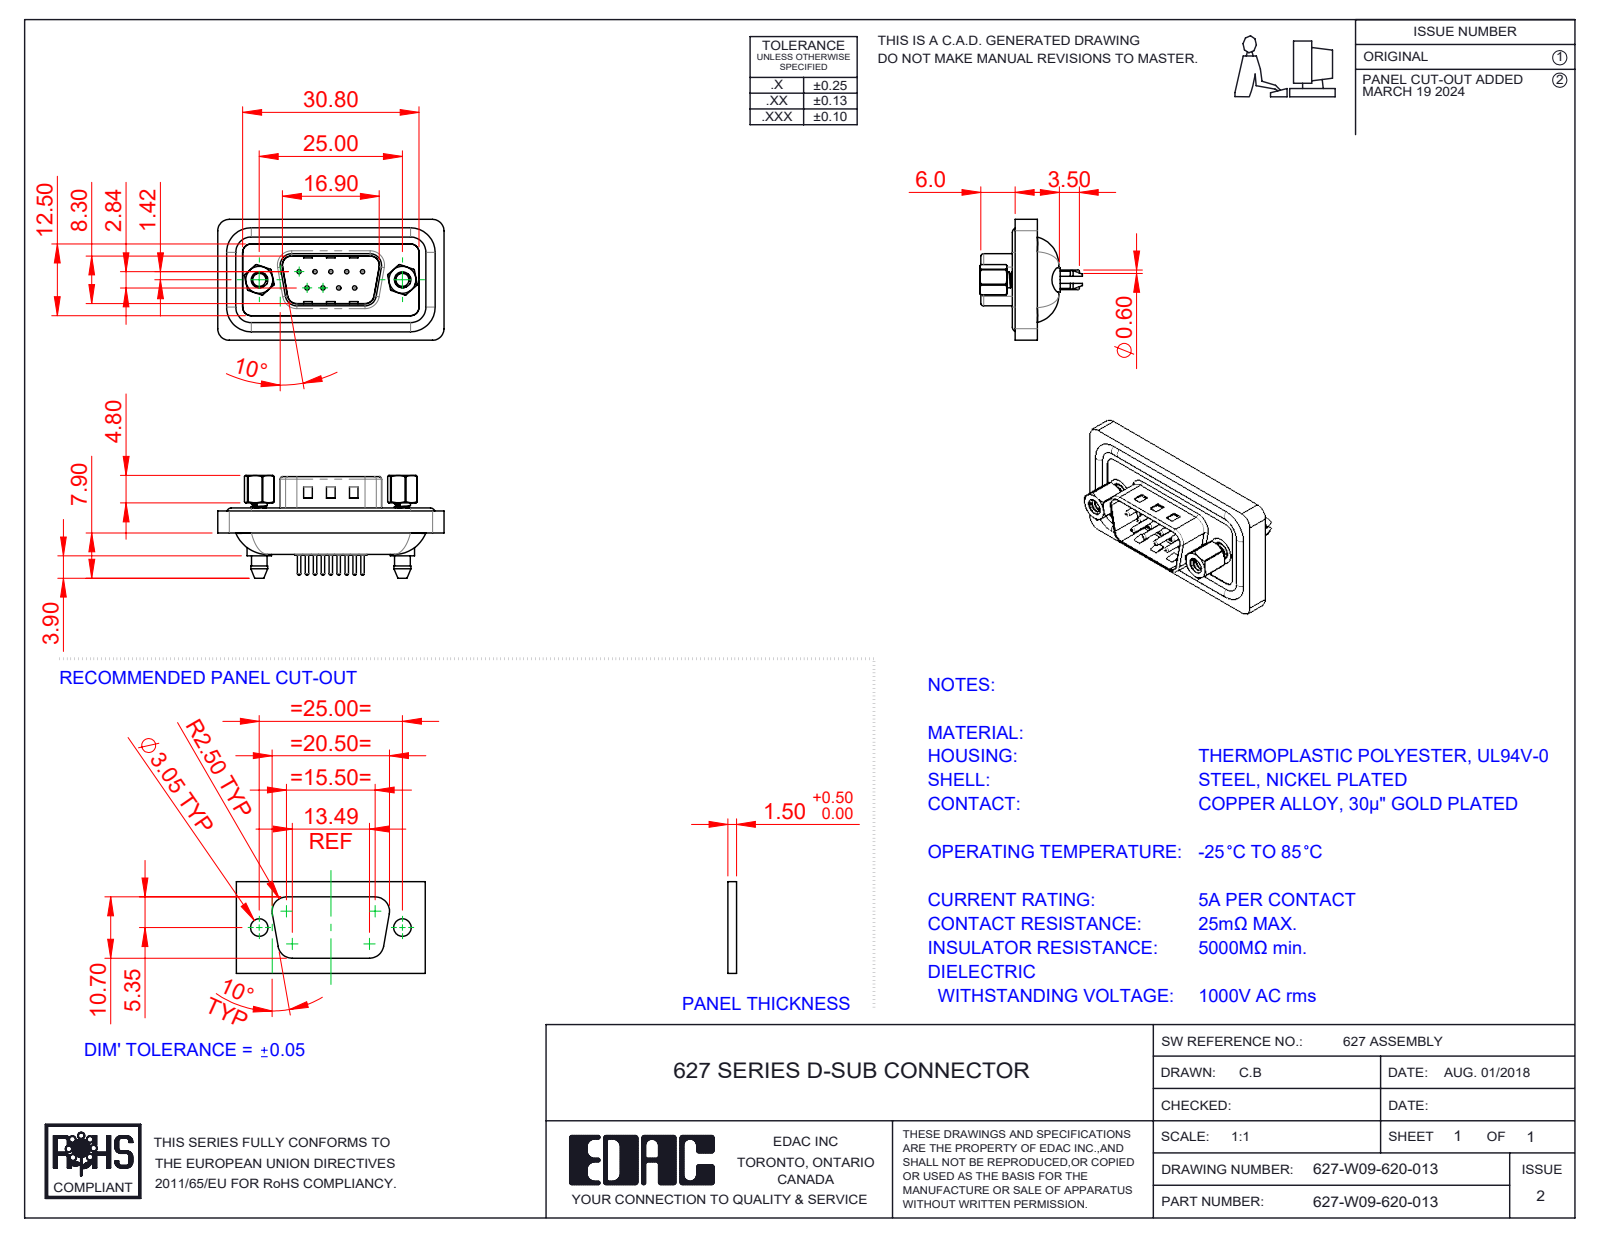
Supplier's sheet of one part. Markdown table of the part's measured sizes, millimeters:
| quantity | value |
| --- | --- |
| part name | 627W Contact Row 2_20; 627W Housing_09 Contacts; 627W Waterproof Housing_09 Contacts BL; 627-W09-620-013 (+4 more) |
| STEP written by | SolidWorks 2020 (CONFIG_CONTROL_DESIGN) |
| units | millimeters |
| bodies | 17 solids, 847 faces (218 planar, 388 cylindrical, 241 other) |
| overall size | 39.5 × 21.1 × 17.75 |
| volume | 4 719 mm³ |
| surface area | 6 930 mm² |
| round holes (diameter × count) | 0.75 × 9, 1.5 × 9, 1.6 × 9, 2 × 9, 2.26 × 2, 2.29 × 2, 4 × 2, 4.25 × 2, 4.8 × 2 |
| round bosses / shafts (diameter × count) | 0.6 × 9, 1.6 × 4, 1.5 × 4, 5.4 × 2, 4.9 × 2, 2.79 × 2 |
| partial cylindrical surfaces (radius × count) | 1.5 × 16, 2 × 16, 0.5 × 8, 1.6 × 6, 0.9 × 4, 2.7 × 4, 4.3 × 4, 0.4 × 2 |
| main face-to-face distances | 0.4, 0.75, 1.1, 2.75, 0.5, 3.75, 1.85, 3.85, 3.35, 1 |
| hole center spacings | 3.16, 2.77, 5.54, 5.03, 5.04, 7.48, 7.49, 8.31 |
